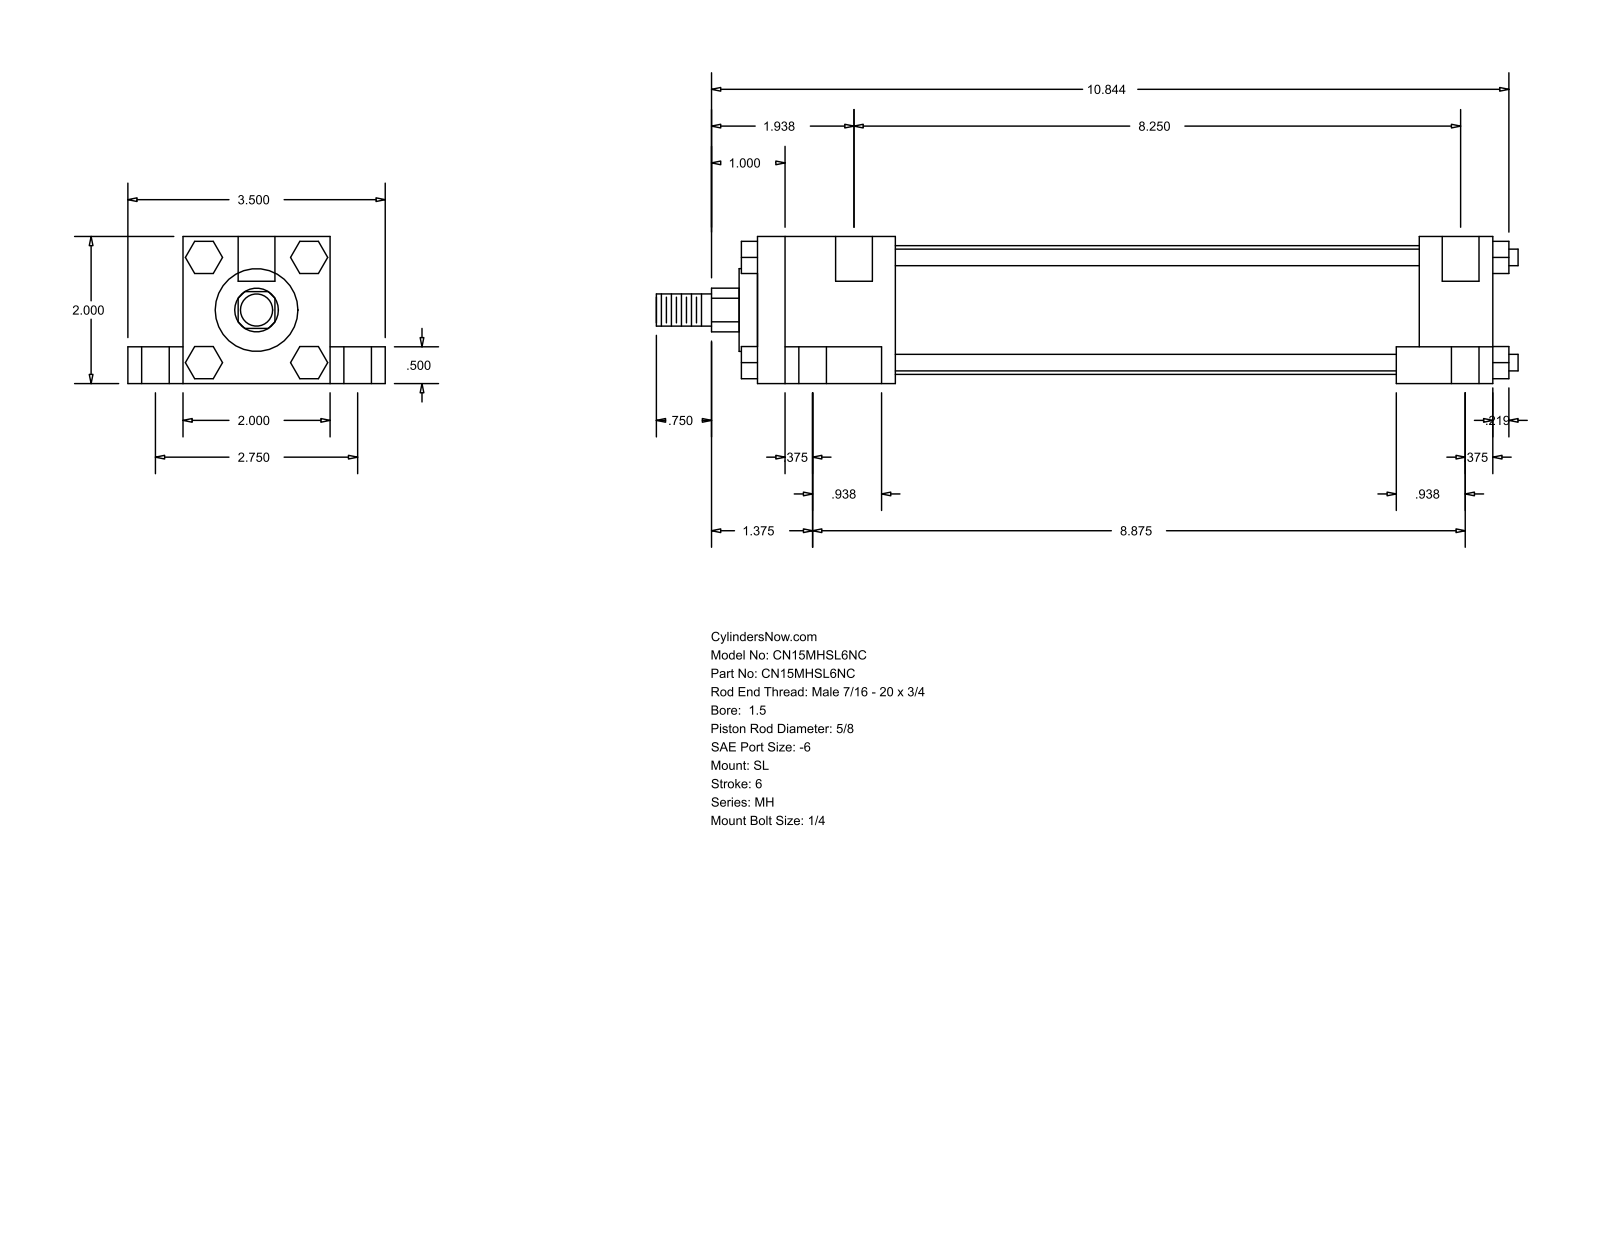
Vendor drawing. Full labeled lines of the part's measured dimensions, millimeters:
Part name (STEP PRODUCT): MH_SL__0150_0.625
STEP written by: GSSL Pune (CONFIG_CONTROL_DESIGN)
Units: millimetres
Bodies: 0 solids, 148 faces (112 planar, 36 cylindrical, 0 other)
Overall size (bounding box): 297.66 × 88.9 × 50.8
Round holes (diameter × count): ⌀5.56 ×4, ⌀9.53 ×4, ⌀15.88 ×4, ⌀12.7 ×2
Round bosses / shafts (diameter × count): ⌀5.71 ×4, ⌀44.45 ×1, ⌀28.57 ×1, ⌀15.88 ×1, ⌀11.11 ×1
Partial cylindrical surfaces — rounded edges, fillets, slot ends (radius × count): R7.54 ×1
Main face-to-face distances: 50.8, 38.1, 19.05, 12.7, 69.85, 254, 9.52, 33.34, 211.14, 228.59
Hole centre spacings: 34.96, 36.65, 37.73, 69.84, 212.72, 214.01, 217.14, 225.43
